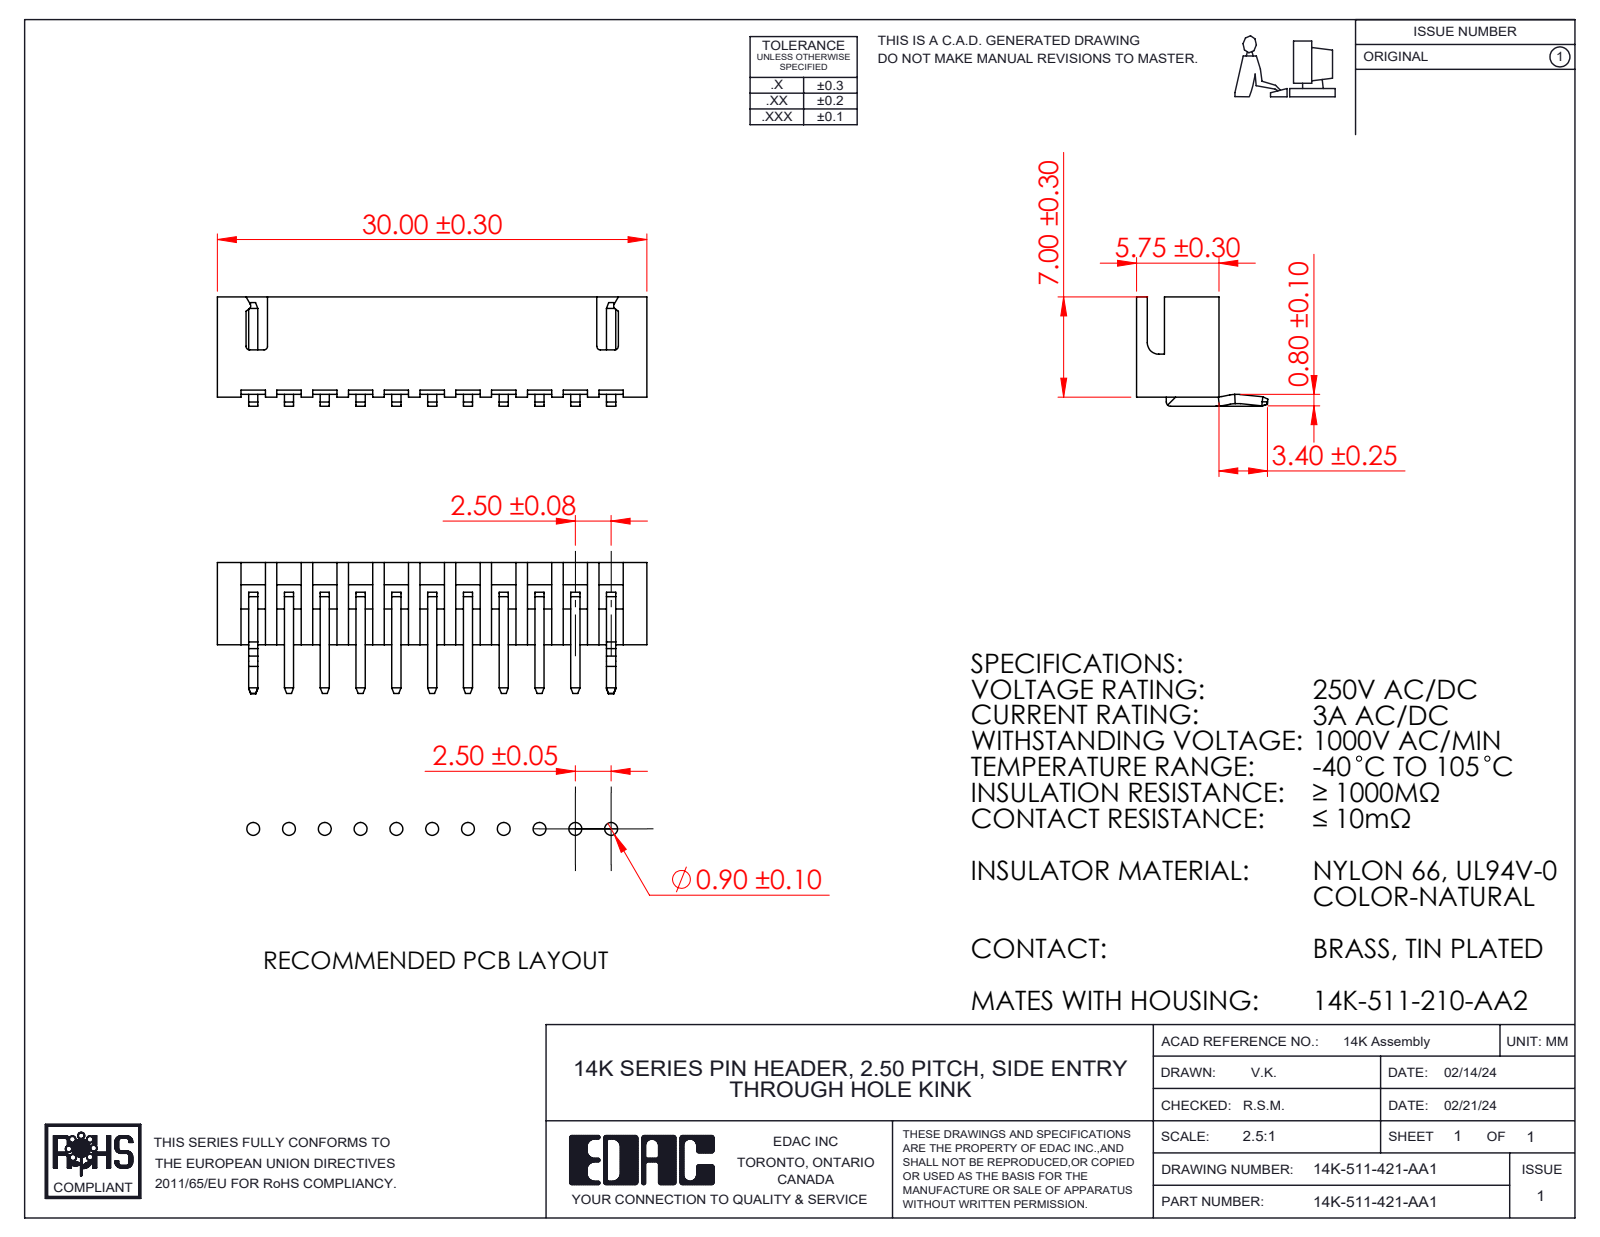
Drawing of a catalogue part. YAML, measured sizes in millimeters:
part_name: "14K-511-421-AA1; 14K Series Pin_21; 14K Series Pin Header Insulator_511; 14K Series Pin_16"
step_written_by: "SolidWorks 2023 (CONFIG_CONTROL_DESIGN)"
units: millimeters
bodies: {solids: 12, faces: 420, planar: 377, cylindrical: 43, other: 0}
overall_size: [30, 9.17, 7.64]
volume: 574
surface_area: 1620
partial_cylinders:
  - {radius: 0.25, count: 6}
  - {radius: 2.5, count: 4}
  - {radius: 0.3, count: 2}
  - {radius: 0.8, count: 1}
face_to_face_distances: [5, 0.76, 5.76, 0.64, 4.24, 2.5, 7.5, 10, 1.95, 1.7]
